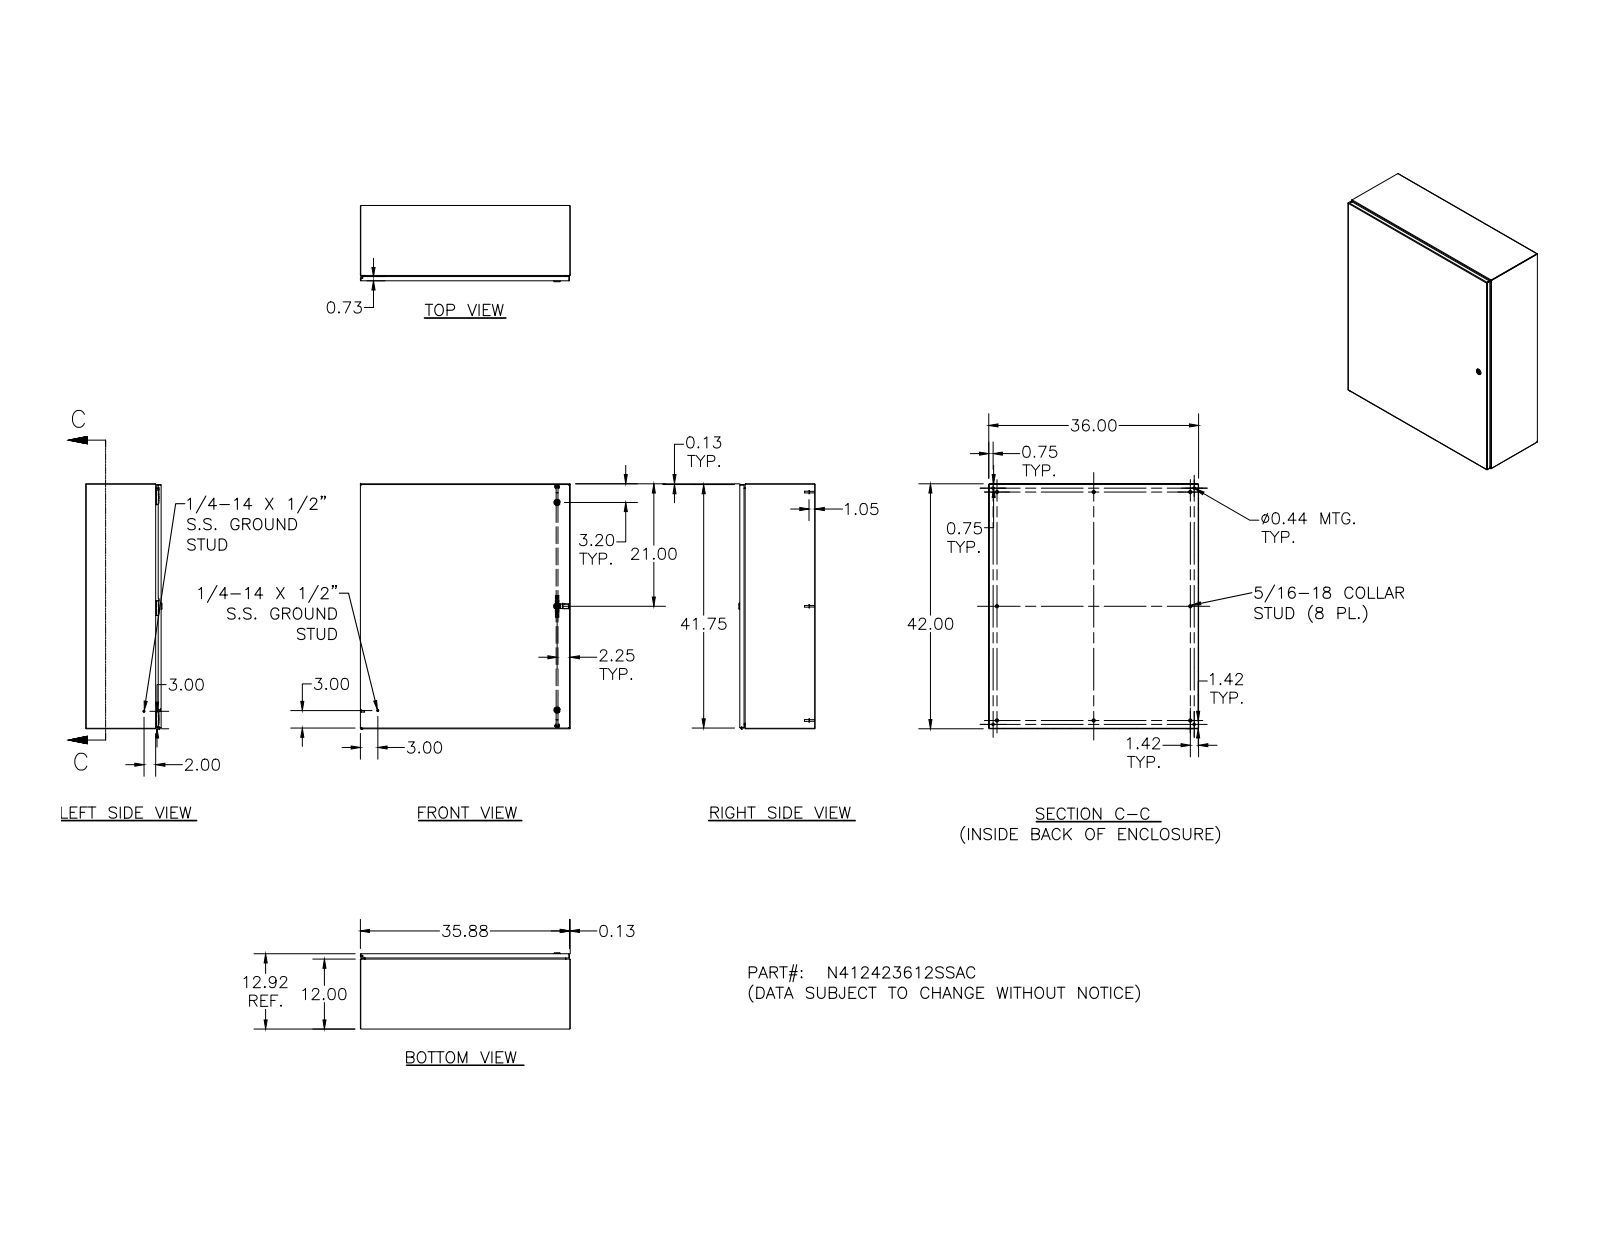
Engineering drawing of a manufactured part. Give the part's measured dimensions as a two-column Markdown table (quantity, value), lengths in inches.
| quantity | value |
| --- | --- |
| part name | N412SSACASSM3PCBTB; N412423612SSACBTB; N4124212SSACLS; N4124212SSACRS (+8 more) |
| STEP written by | Autodesk Inventor 2012 (AUTOMOTIVE_DESIGN) |
| units | inches |
| bodies | 72 solids, 2233 faces (865 planar, 818 cylindrical, 550 other) |
| overall size | 42 × 36 × 13.075 |
| volume | 389.9 in³ |
| surface area | 10 520 in² |
| round holes (diameter × count) | 0.093 × 6, 0.152 × 6, 0.167 × 6, 0.172 × 6, 0.187 × 6, 0.197 × 5, 0.165 × 4, 0.437 × 4, 0.156 × 3, 0.106 × 2, 0.16 × 2, 0.169 × 2 |
| round bosses / shafts (diameter × count) | 0.25 × 14, 0.563 × 8, 0.3 × 8, 0.275 × 8, 0.36 × 6, 0.32 × 6, 0.256 × 6, 0.164 × 6 |
| partial cylindrical surfaces (radius × count) | 0.05 × 38, 0.031 × 32, 0.012 × 30, 0.016 × 26, 0.125 × 24, 0.02 × 20, 0.105 × 18, 0.118 × 16 |
| main face-to-face distances | 0.074, 12.843, 12.769, 12.917, 35.926, 41.926, 35.852, 36, 41.852, 42 |
| hole center spacings | 19, 38, 19.007, 0.5, 0.656, 0.66, 1.307, 1.311 |
